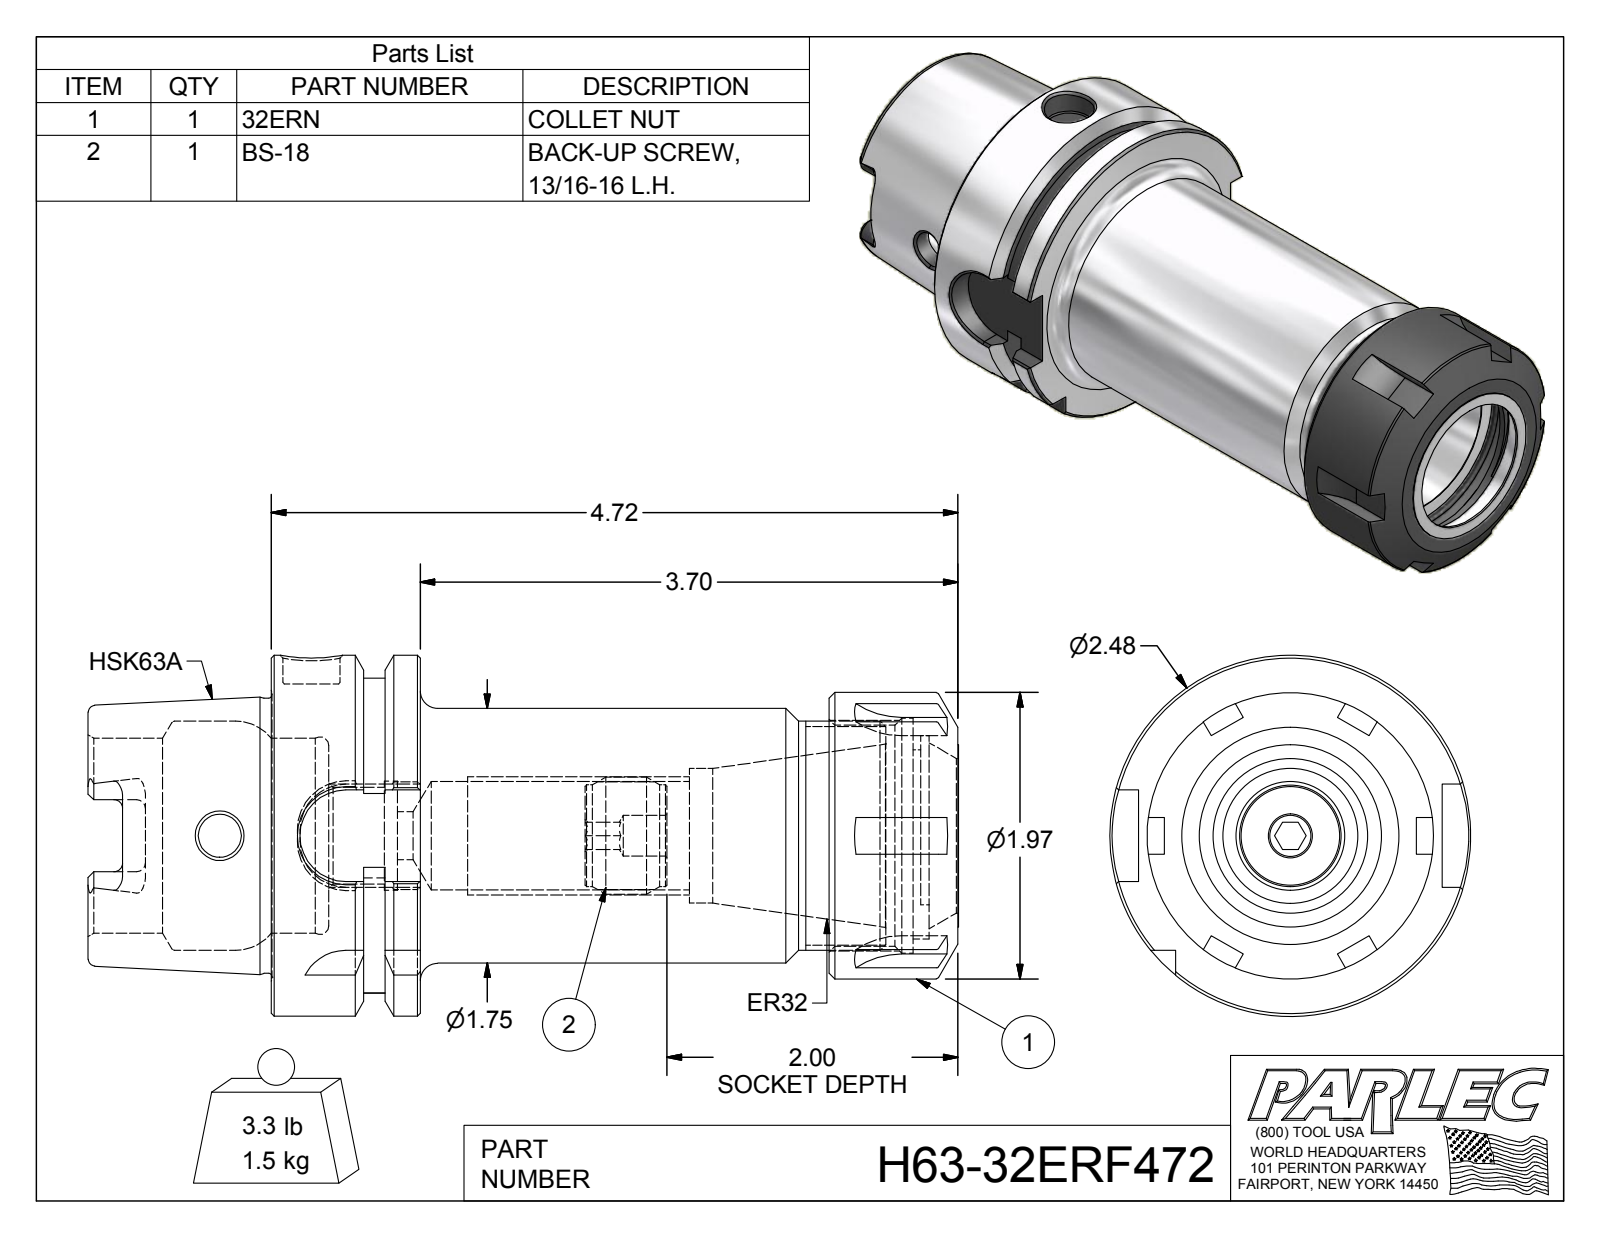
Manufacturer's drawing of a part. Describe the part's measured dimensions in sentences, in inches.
The part is named "H63-32ER5-1; 32ERN; BS-18; H63-32ERF472". Its 3-D file was written by "Autodesk Inventor 2016 (AUTOMOTIVE_DESIGN)". It is 3 solids with 241 faces: 95 planar, 60 cylindrical and 86 other. Overall it measures 5.98 by 2.48 by 2.48 inches. Its volume is 11.67 cubic inches and its surface area 76 square inches. Round holes: 1 of diameter 0.28, 1 of diameter 0.295, 1 of diameter 0.331, 1 of diameter 0.394, 1 of diameter 0.666, 1 of diameter 0.745, 1 of diameter 0.749, 1 of diameter 0.925, 1 of diameter 1.063, 1 of diameter 1.3, 1 of diameter 1.339, 1 of diameter 1.522. Round bosses or shafts: 1 of diameter 2.48, 1 of diameter 1.969, 1 of diameter 1.891, 1 of diameter 1.75, 1 of diameter 0.805, 1 of diameter 0.7. Partial cylindrical surfaces (rounded edges, fillets, slot ends): 12 of radius 0.02, 6 of radius 0.059, 4 of radius 0.113, 4 of radius 0.315, 1 of radius 0.587, 1 of radius 0.689, 1 of radius 1.083. The main face-to-face distances are 1.024, 4.72, 3.696, 0.394, 0.63, 4.326, 3.823, 3.43, 2.8, 0.897. The hole center spacings are 0.073.
